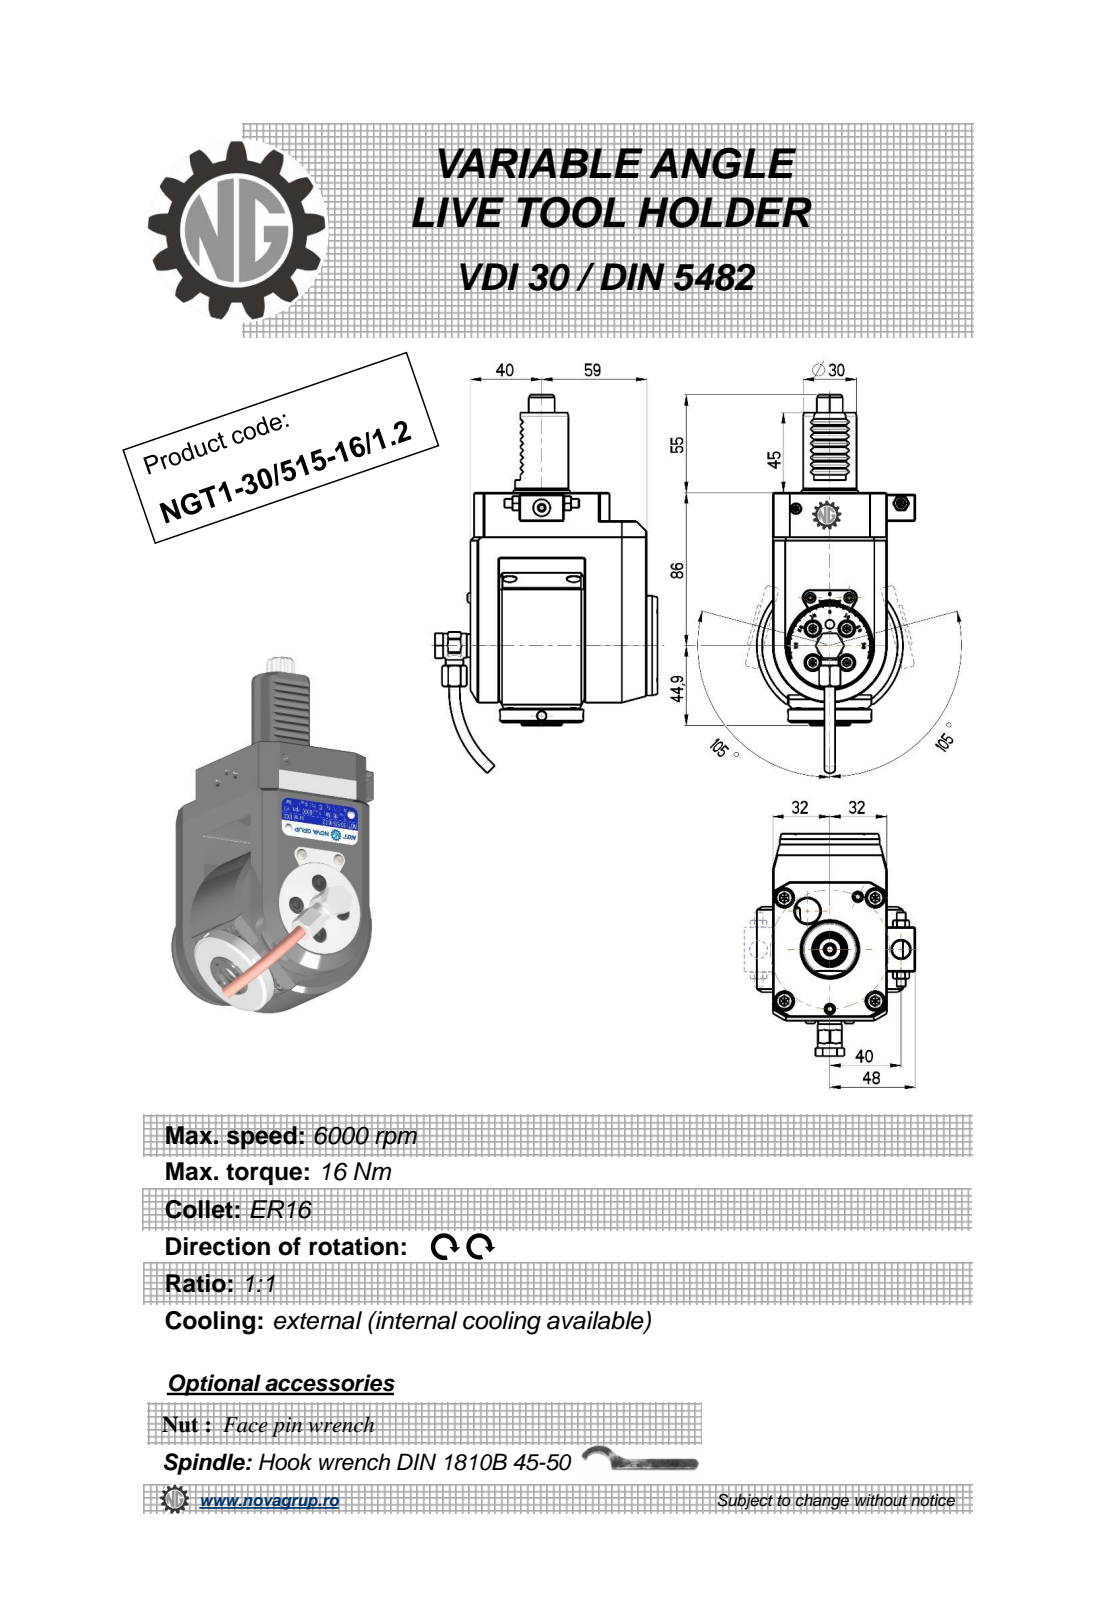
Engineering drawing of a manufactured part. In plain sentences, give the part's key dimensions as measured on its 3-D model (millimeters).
The part is named "NGT1_30_515_16_1_2". Its 3-D file was written by "PRO/ENGINEER BY PARAMETRIC TECHNOLOGY CORPORATION, 2010280 (CONFIG_CONTROL_DESIGN)". It is 1 solid with 506 faces: 181 planar, 160 cylindrical and 165 other. Overall it measures 212.67 by 124.9 by 89 millimeters. Its volume is 752 981 cubic millimeters and its surface area 70 658 square millimeters. Round holes: 4 of diameter 3.2, 3 of diameter 4, 2 of diameter 4.2, 2 of diameter 5, 2 of diameter 10, 1 of diameter 3, 1 of diameter 4.5, 1 of diameter 5.3, 1 of diameter 6.2, 1 of diameter 9, 1 of diameter 9.5, 1 of diameter 11. Round bosses or shafts: 2 of diameter 6, 2 of diameter 5.7, 1 of diameter 82, 1 of diameter 56, 1 of diameter 47, 1 of diameter 35, 1 of diameter 30, 1 of diameter 23. Partial cylindrical surfaces (rounded edges, fillets, slot ends): 16 of radius 2.91, 12 of radius 0.26, 8 of radius 0.3, 4 of radius 0.5, 2 of radius 1, 1 of radius 5.75, 1 of radius 7.25, 1 of radius 7.7. The main face-to-face distances are 64, 16, 37, 99, 6, 105, 21, 14, 35, 48. The hole center spacings are 9.25, 13.08, 18.5, 41.06, 49.87, 50.26, 0.4, 30.75.
